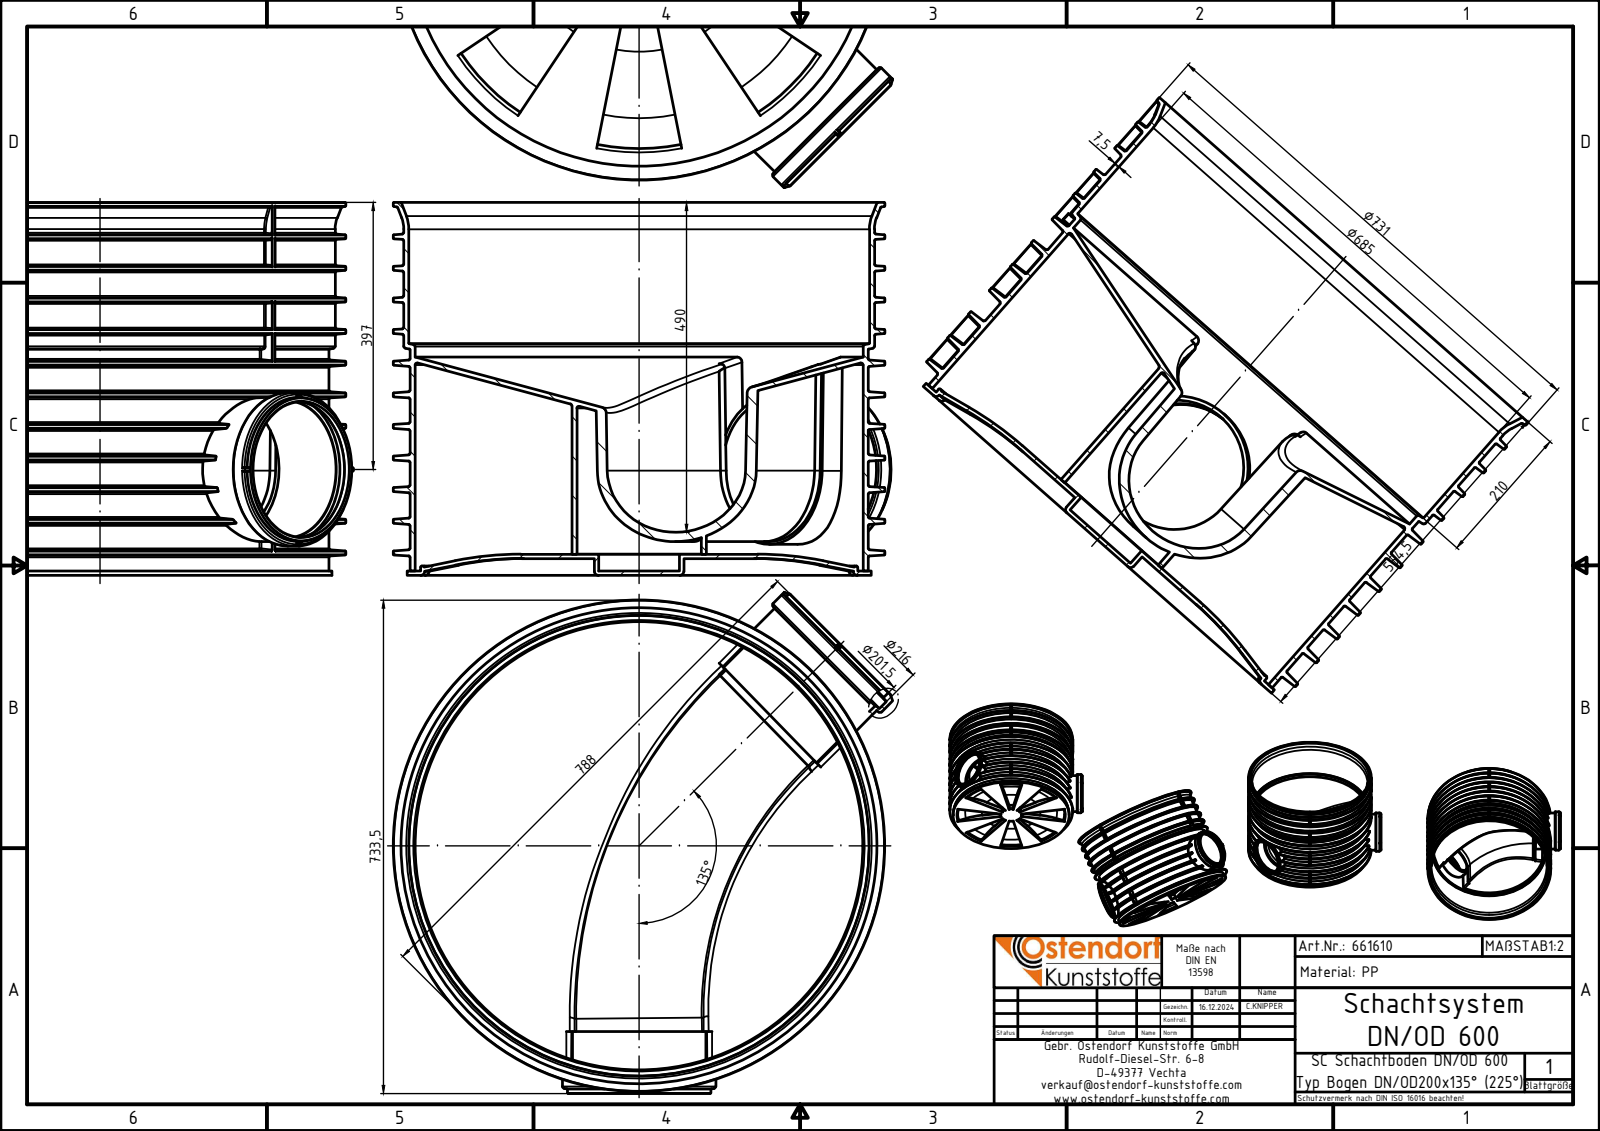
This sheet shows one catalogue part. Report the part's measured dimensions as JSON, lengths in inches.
{"part_name": "661610z; 661610 Schacht DN600 Boden; 661610 Schachtboden DN600 Grundkörper", "step_written_by": "Autodesk Inventor 2024 (AUTOMOTIVE_DESIGN)", "units": "inches", "bodies": {"solids": 2, "faces": 1408, "planar": 203, "cylindrical": 227, "other": 978}, "overall_size": [29.324, 29.225, 21.831], "volume_in3": 1566, "surface_area_in2": 8652, "round_holes": [[7.933, 3], [8.504, 2], [4.724, 1], [7.283, 1], [7.35, 1], [25.197, 1], [26.22, 1], [26.969, 1]], "round_bosses_or_shafts": [[8.976, 2], [8.406, 2], [28.78, 1], [27.559, 1], [27.165, 1], [26.811, 1], [25.591, 1], [8.445, 1]], "partial_cylinders_radius": [[0.039, 24], [0.079, 16], [0.059, 4], [0.031, 2], [4.384, 2], [2.618, 1], [4.222, 1], [12.539, 1]], "face_to_face_distances": [0.256, 0.984, 1.24, 0.728, 21.831, 21.575, 20.846, 20.591, 0.512, 0.547]}
